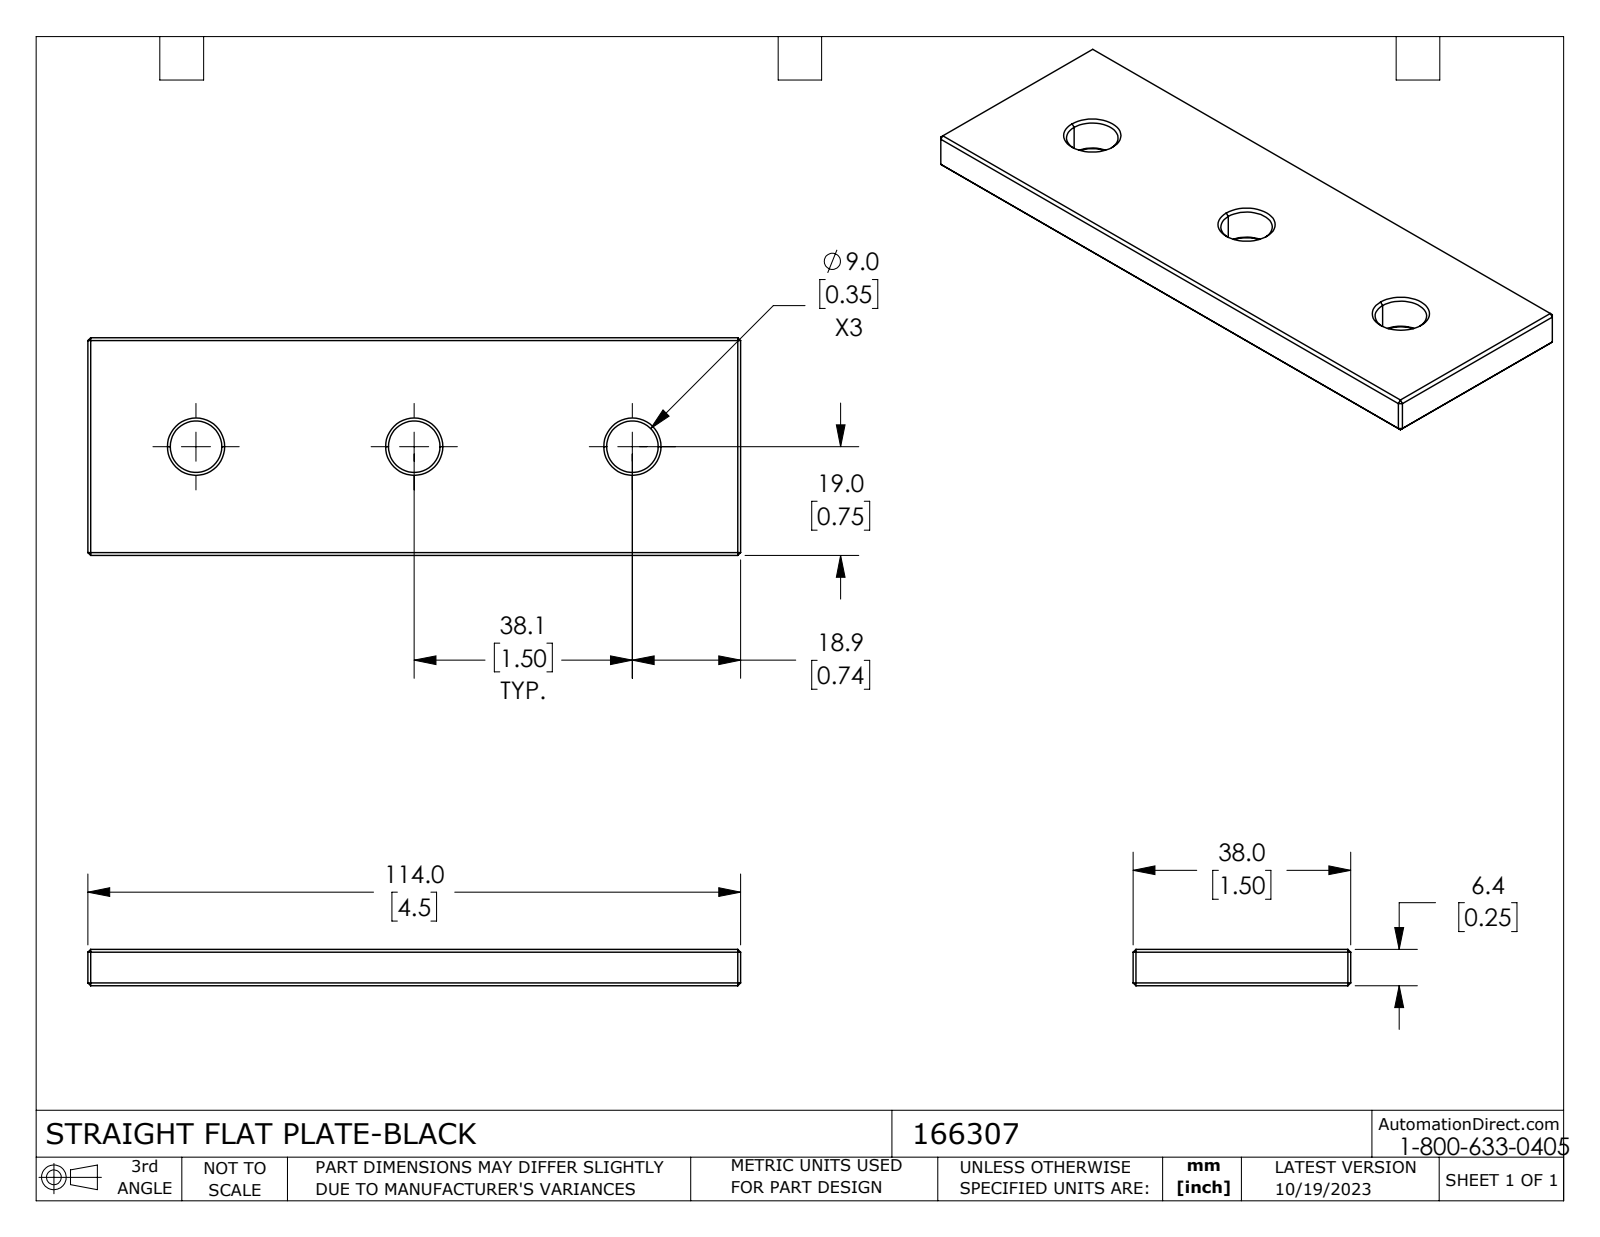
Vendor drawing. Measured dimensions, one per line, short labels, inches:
name: 166307
written by: SolidWorks 2023 (CONFIG_CONTROL_DESIGN)
unit: in
bodies: 1 solid, 44 faces (26 planar, 6 cylindrical, 12 other)
size: 4.488 × 1.496 × 0.25
volume: 1.599 in³; area: 16.3 in²
holes: 3× ⌀0.354
face distances: 0.25, 1.496, 4.488, 1.207, 3.322, 4.203, 3.552, 3.552
hole spacings: 1.5, 3
